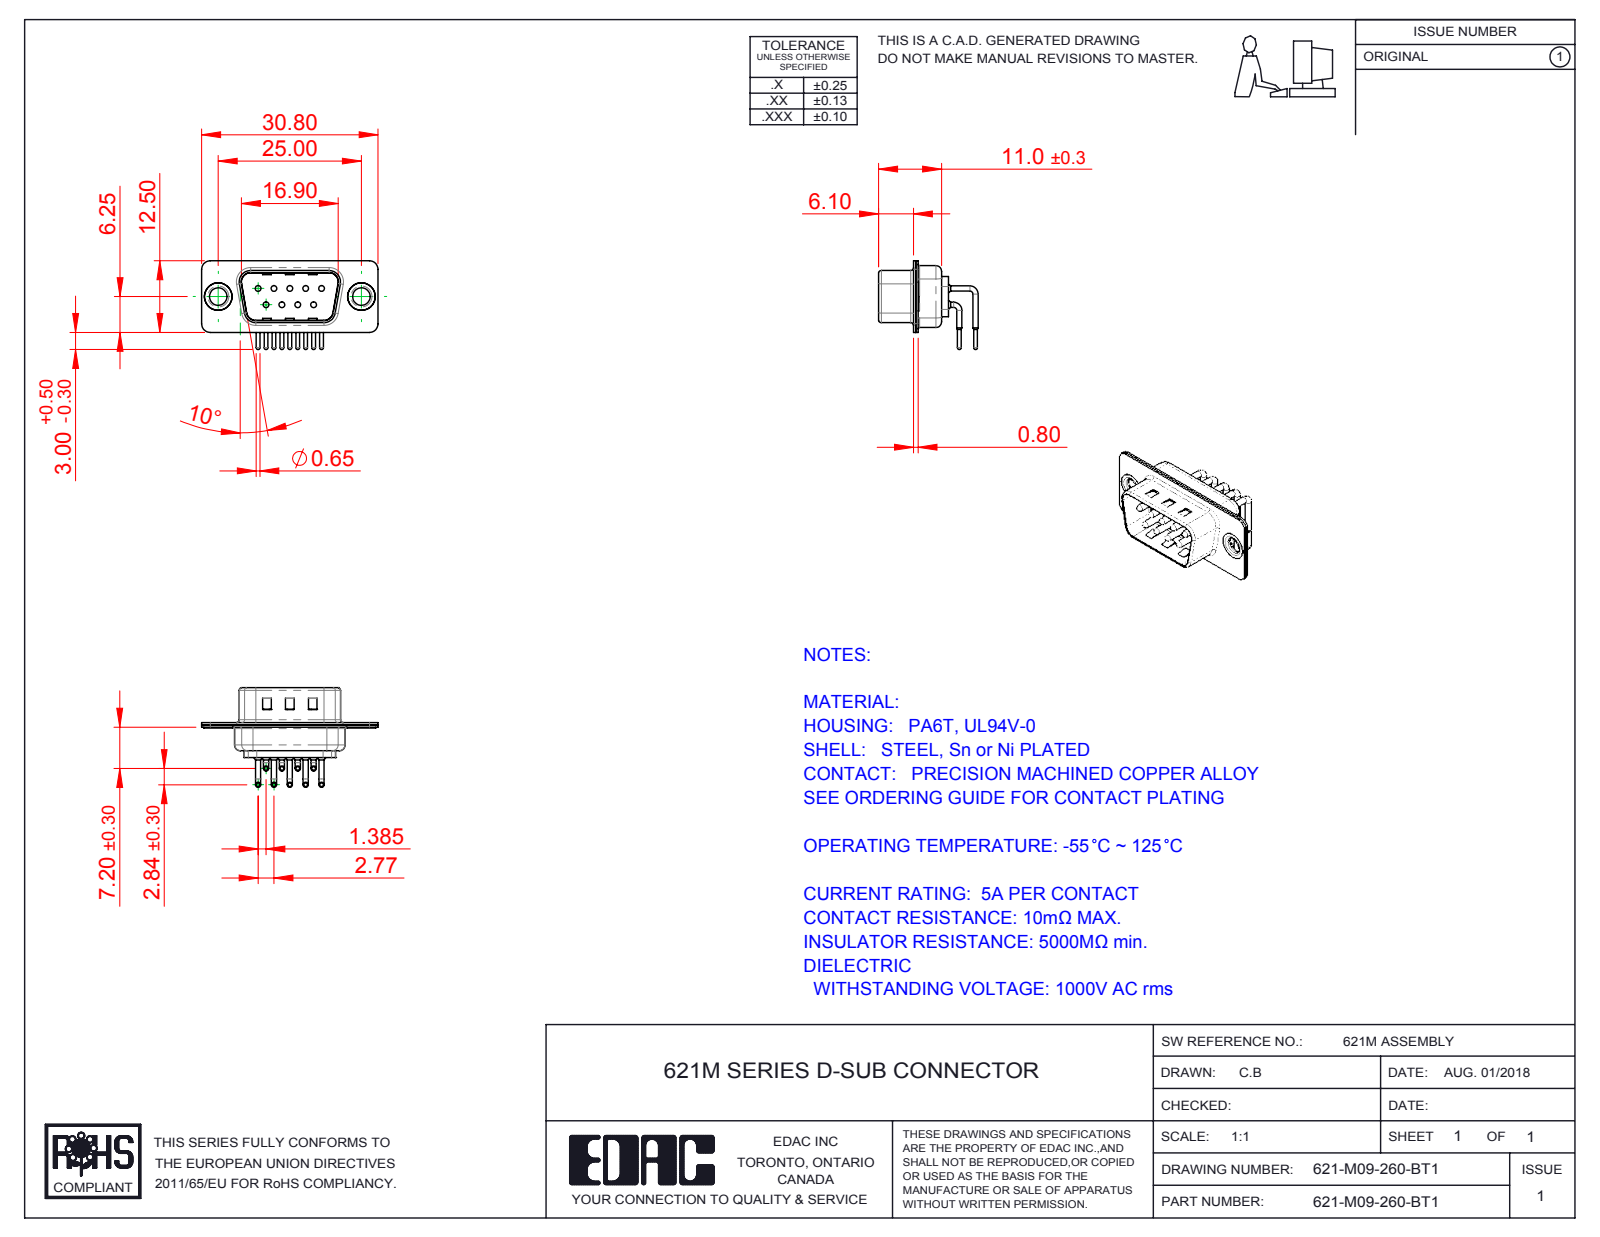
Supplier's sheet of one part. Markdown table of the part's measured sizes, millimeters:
| quantity | value |
| --- | --- |
| part name | 621M Thru Hole Rivet; 621M Shell Front_09 Contacts; 621-M09-260-BT1; 621M Housing_09 Contacts (+3 more) |
| STEP written by | SolidWorks 2016 (CONFIG_CONTROL_DESIGN) |
| units | millimeters |
| bodies | 14 solids, 1268 faces (683 planar, 437 cylindrical, 148 other) |
| overall size | 30.8 × 17.39 × 15.49 |
| volume | 1 289 mm³ |
| surface area | 3 701 mm² |
| round holes (diameter × count) | 1 × 9, 1.7 × 9, 2 × 9, 3.05 × 2, 4 × 2, 4.8 × 2 |
| round bosses / shafts (diameter × count) | 0.9 × 18, 1.5 × 9, 0.65 × 9, 5 × 2, 4.9 × 2, 3.55 × 2 |
| partial cylindrical surfaces (radius × count) | 1.5 × 16, 2 × 12, 1.01 × 9, 0.5 × 8, 1.6 × 8, 0.25 × 4, 0.6 × 4, 0.65 × 4 |
| main face-to-face distances | 0.4, 0.85, 0.8, 9.55, 1.25, 10.4, 8.7, 0.35, 6.1, 5.7 |
| hole center spacings | 3.16, 2.77, 5.54, 5.03, 5.04, 8.31, 7.1, 7.48 |
